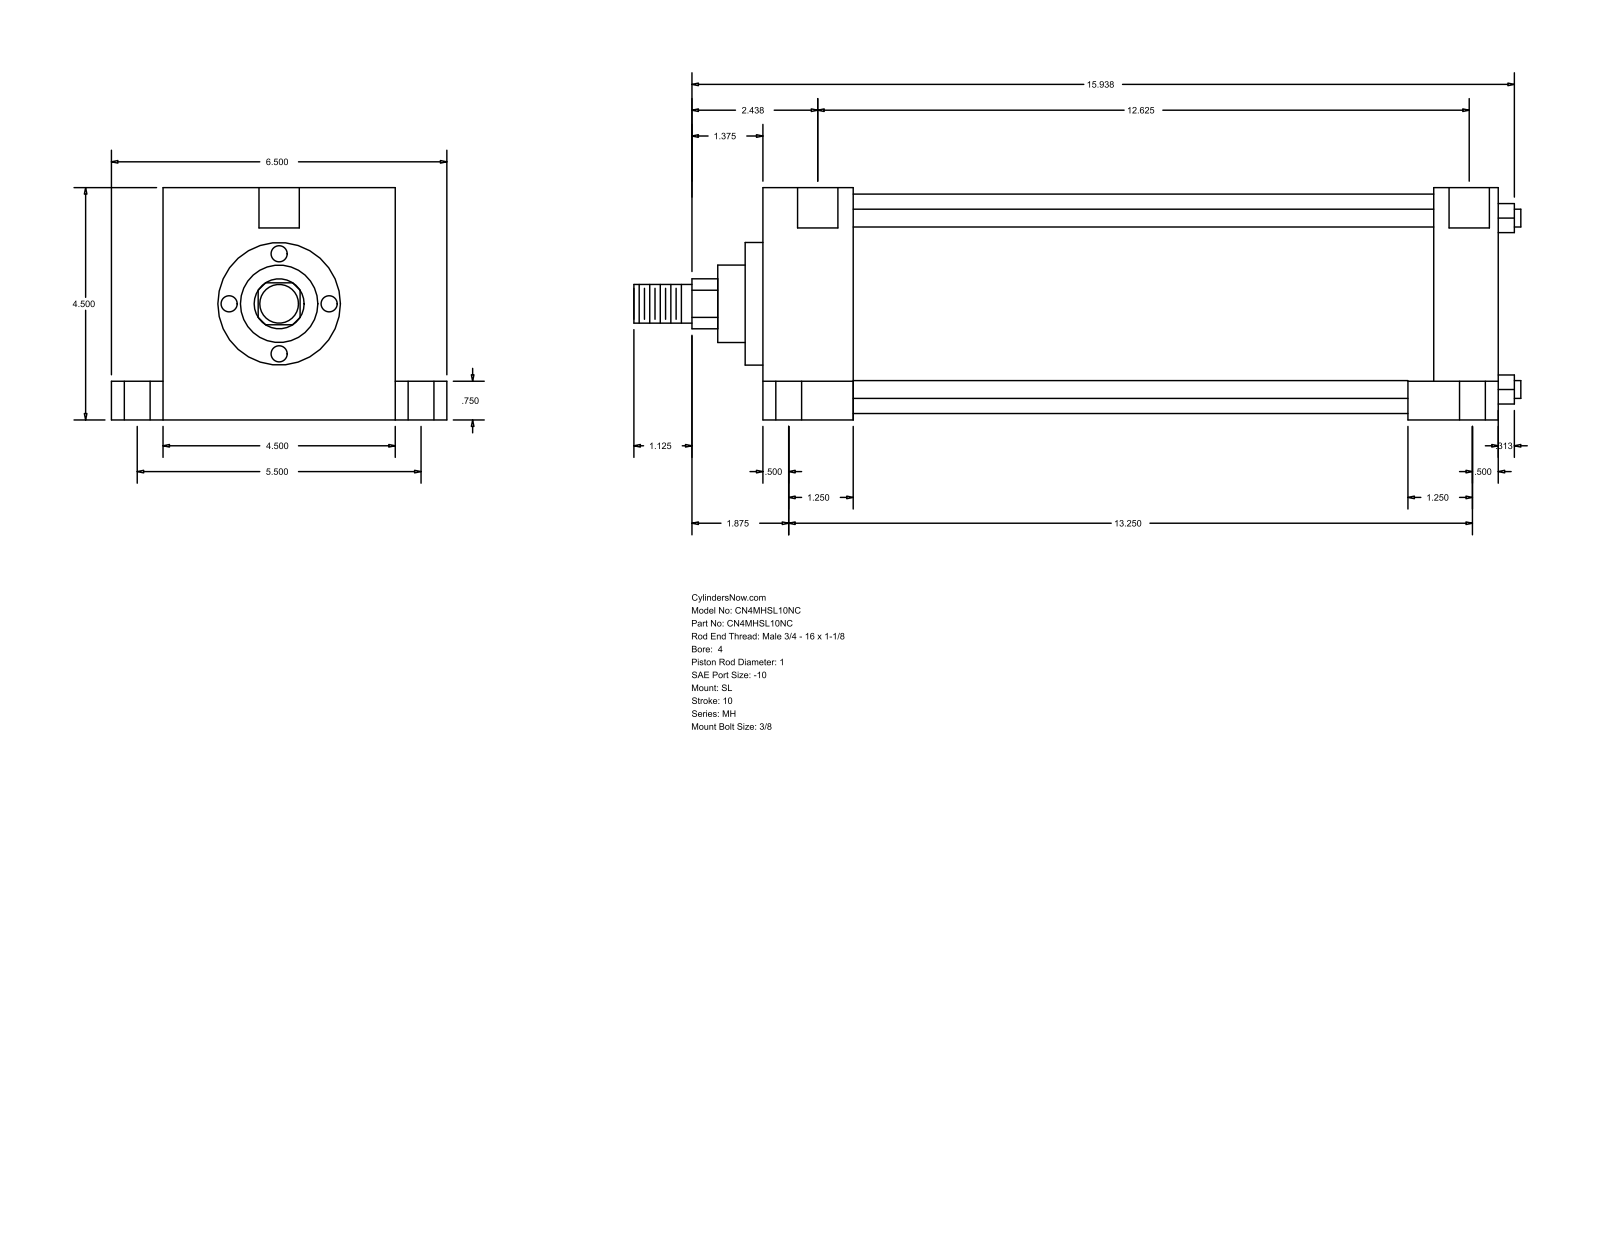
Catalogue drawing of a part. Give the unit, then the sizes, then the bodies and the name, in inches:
Units: inches
Overall size (bounding box): 17.187 × 6.5 × 4.5
Round holes (diameter × count): ⌀0.344 ×4, ⌀0.5 ×4, ⌀0.75 ×4, ⌀0.781 ×2
Round bosses / shafts (diameter × count): ⌀0.345 ×4, ⌀4.25 ×1, ⌀2.375 ×1, ⌀1.5 ×1, ⌀1 ×1, ⌀0.75 ×1
Partial cylindrical surfaces — rounded edges, fillets, slot ends (radius × count): R0.484 ×1
Main face-to-face distances: 4.5, 14.25, 1.75, 12.5, 13, 11.25, 1.25, 1, 5.5, 0.75
Hole centre spacings: 2.75, 2.751, 2.795, 2.807, 5.5, 12.75, 12.982, 13.043
Bodies: 0 solids, 110 faces (77 planar, 33 cylindrical, 0 other)
Part name (STEP PRODUCT): MH_SL__0400_1
STEP written by: GSSL Pune (CONFIG_CONTROL_DESIGN)
